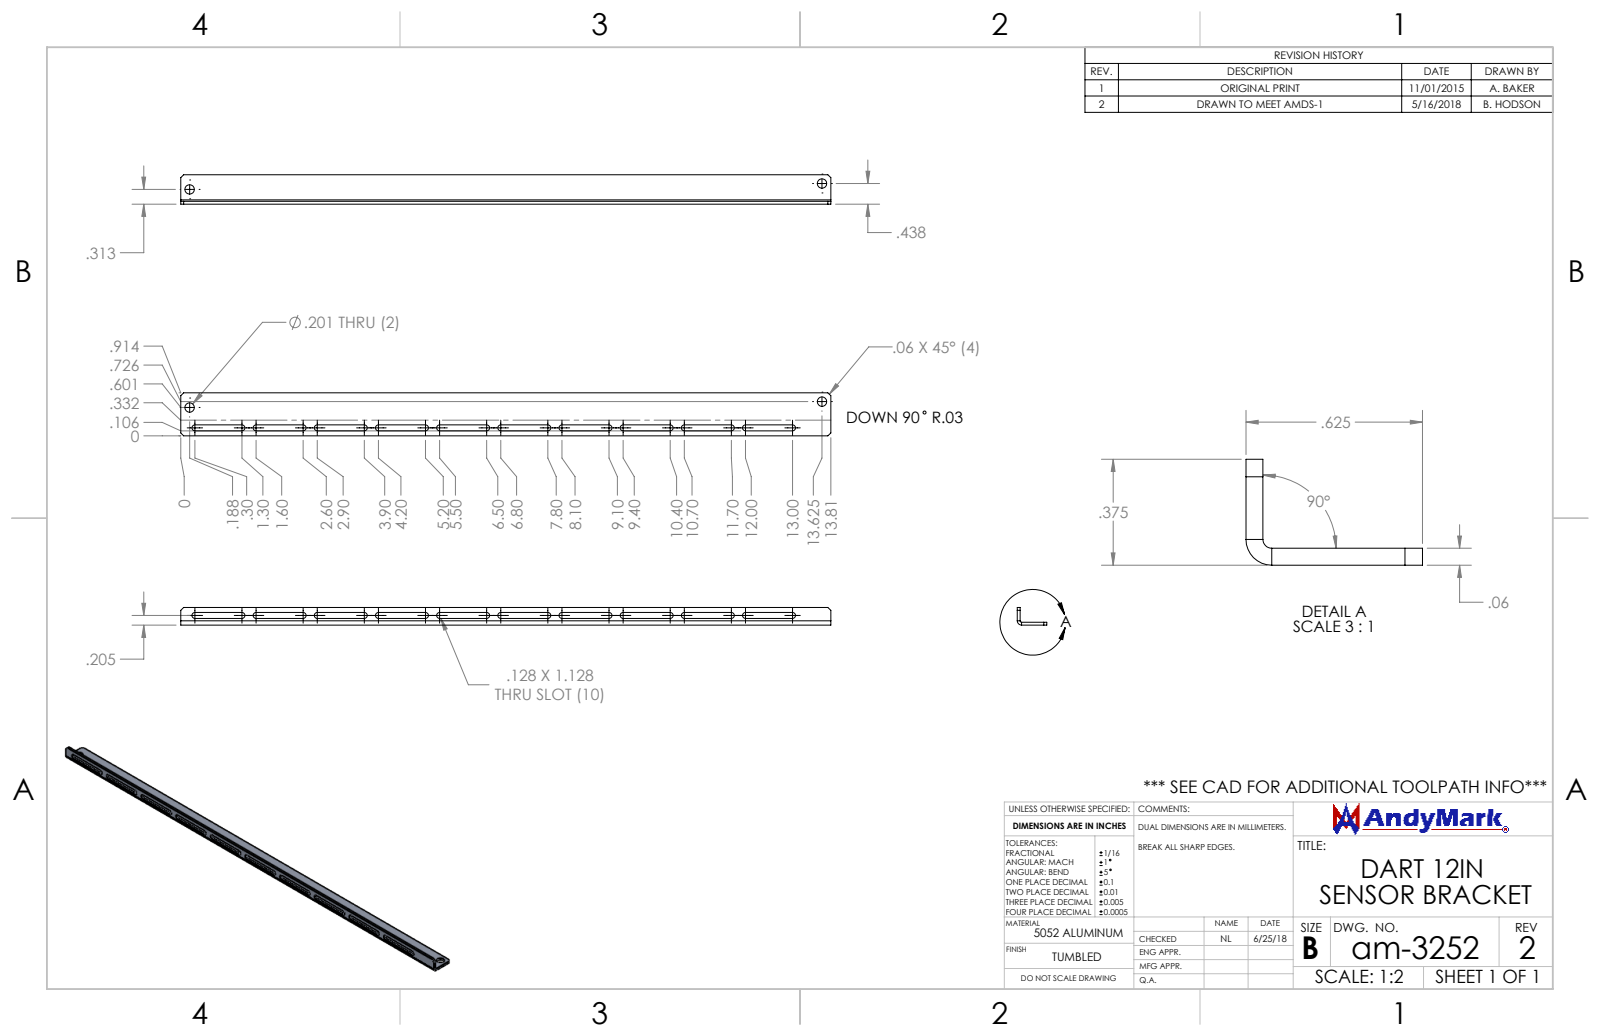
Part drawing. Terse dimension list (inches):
name: am-3252 DART 12 Sensor Bracket REV2
written by: SolidWorks 2017 (AUTOMOTIVE_DESIGN)
unit: in
bodies: 1 solid, 72 faces (36 planar, 36 cylindrical, 0 other)
size: 13.812 × 0.625 × 0.375
volume: 0.669 in³; area: 25.56 in²
holes: 2× ⌀0.201
rounds: 20× R0.064, 1× R0.031, 1× R0.091
face distances: 0.06, 0.06, 0.375, 0.315, 0.565, 0.625, 0.141, 0.081, 0.234, 0.269
hole spacings: 13.438
